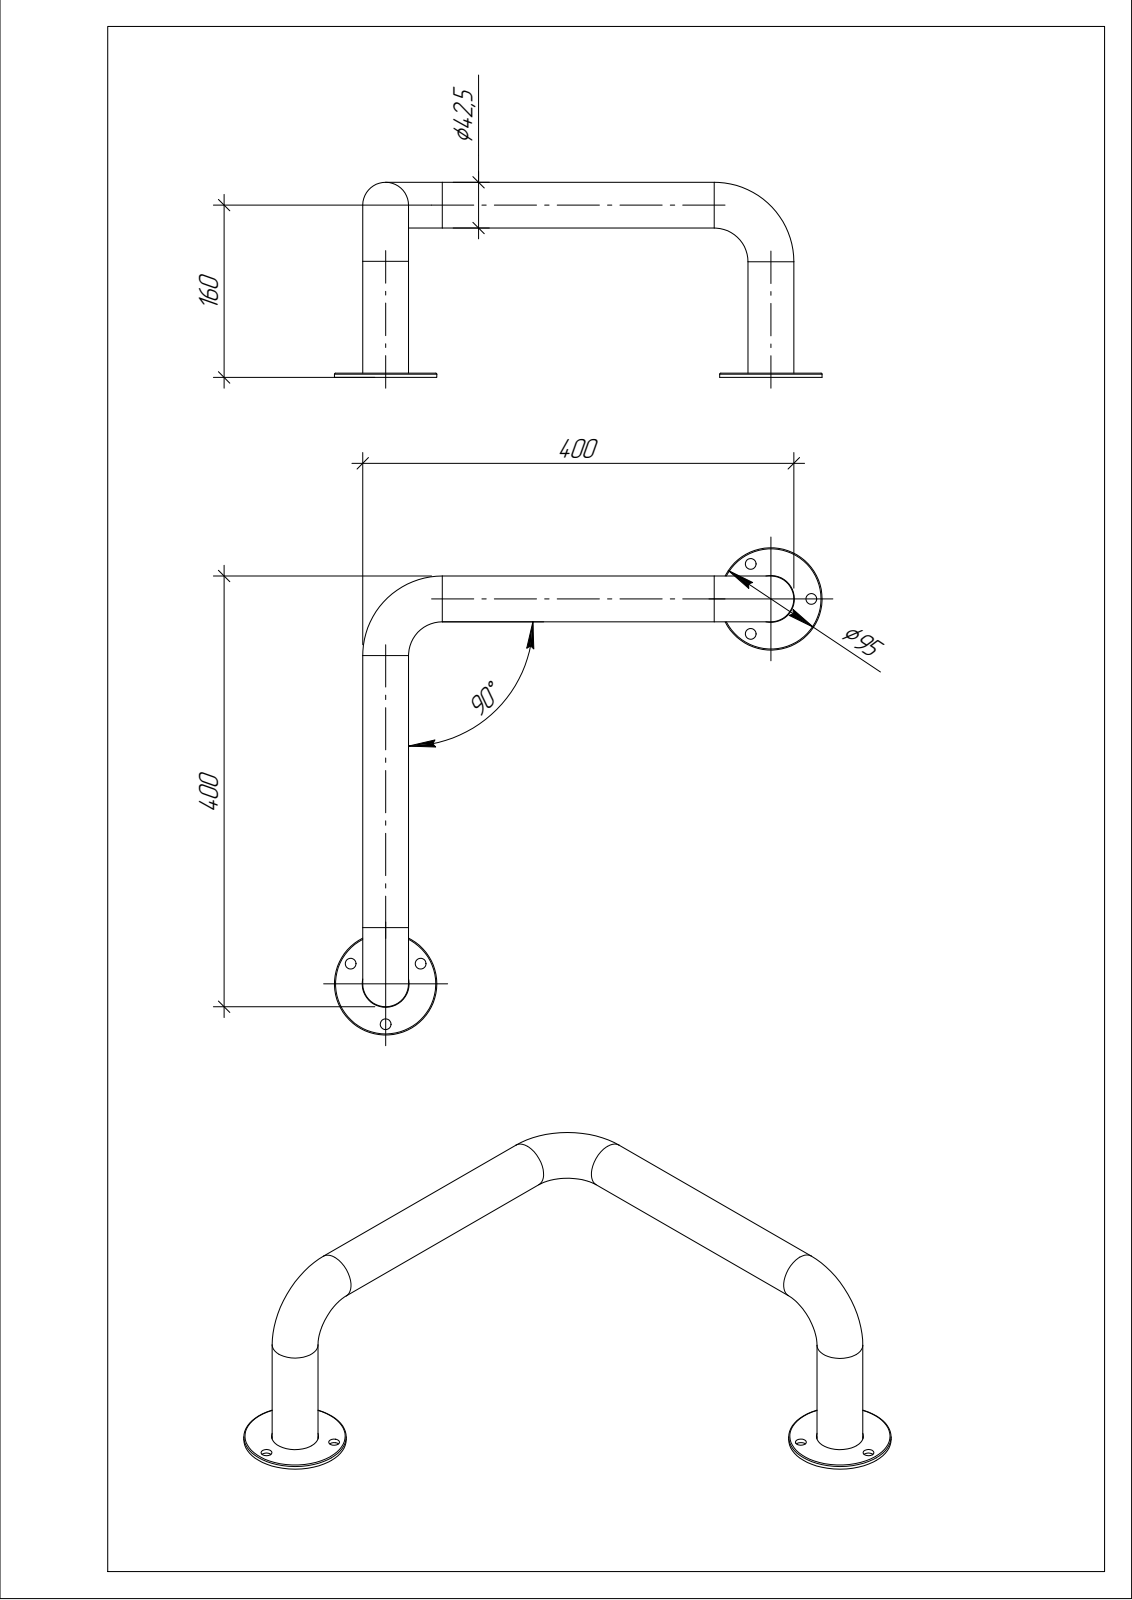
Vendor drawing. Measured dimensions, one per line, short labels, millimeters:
name: Сборка
written by: ASCON Math Kernel (AUTOMOTIVE_DESIGN)
unit: mm
bodies: 3 solids, 25 faces (6 planar, 14 cylindrical, 5 other)
size: 452.5 × 452.5 × 181.25
volume: 1 415 000 mm³; area: 157 452 mm²
holes: 6× ⌀10, 2× ⌀43.5
bosses: 4× ⌀42.5, 2× ⌀95
face distances: 4
hole spacings: 37.5, 64.95, 64.96, 469.46, 481.26, 496.16, 516.56, 532.76
